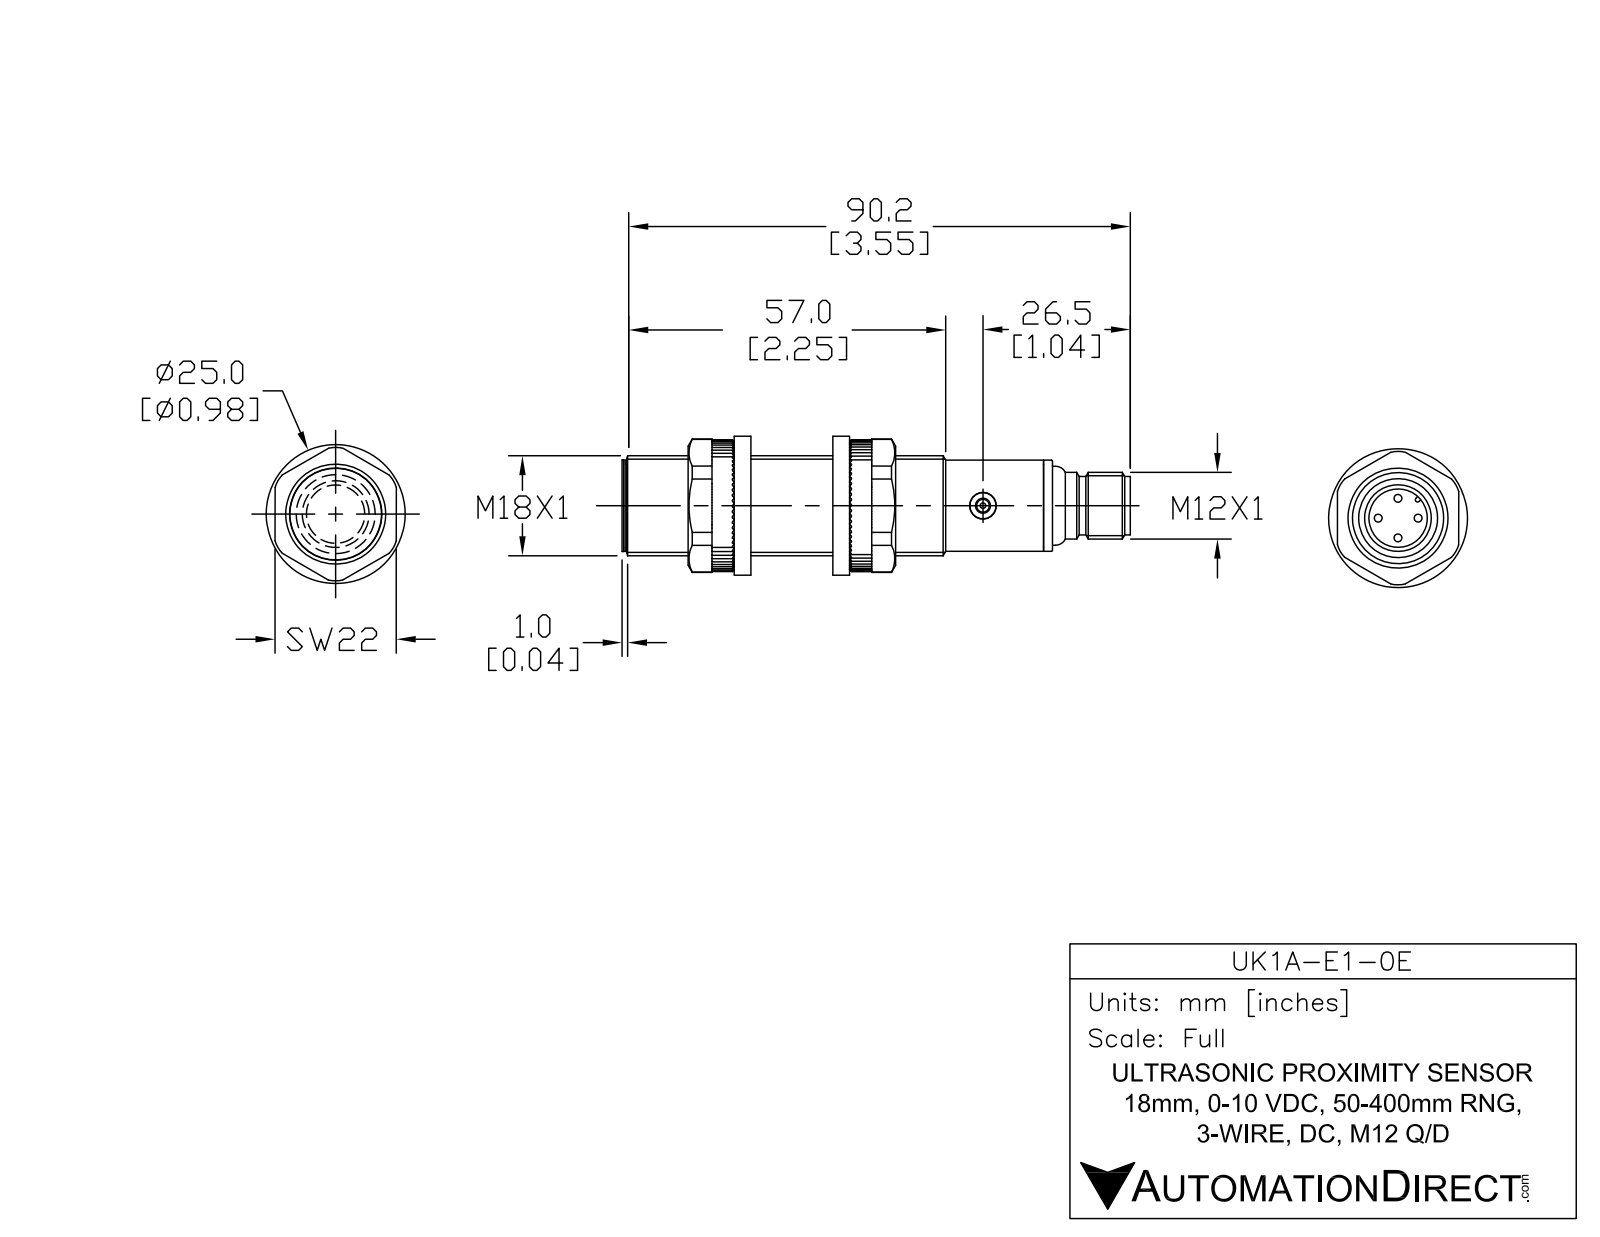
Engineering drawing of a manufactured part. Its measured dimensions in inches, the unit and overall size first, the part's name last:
Units: inches
Overall size (bounding box): 3.606 × 0.709 × 0.709
Round holes (diameter × count): ⌀0.106 ×1, ⌀0.185 ×1, ⌀0.276 ×1, ⌀0.327 ×1, ⌀0.374 ×1
Round bosses / shafts (diameter × count): ⌀0.039 ×4, ⌀0.709 ×1, ⌀0.654 ×1, ⌀0.646 ×1, ⌀0.622 ×1, ⌀0.559 ×1, ⌀0.472 ×1, ⌀0.413 ×1
Partial cylindrical surfaces — rounded edges, fillets, slot ends (radius × count): R0.024 ×1
Main face-to-face distances: 2.957, 0.039, 2.996, 0.037, 2.994, 0.043, 0.157, 3.055, 3.053, 3.016
Volume: 1.202 in³ · Surface area: 10.68 in²
Bodies: 6 solids, 106 faces (21 planar, 48 cylindrical, 37 other)
Part name (STEP PRODUCT): UK1A-E1-0E
STEP written by: SolidWorks 2017 (AUTOMOTIVE_DESIGN)
